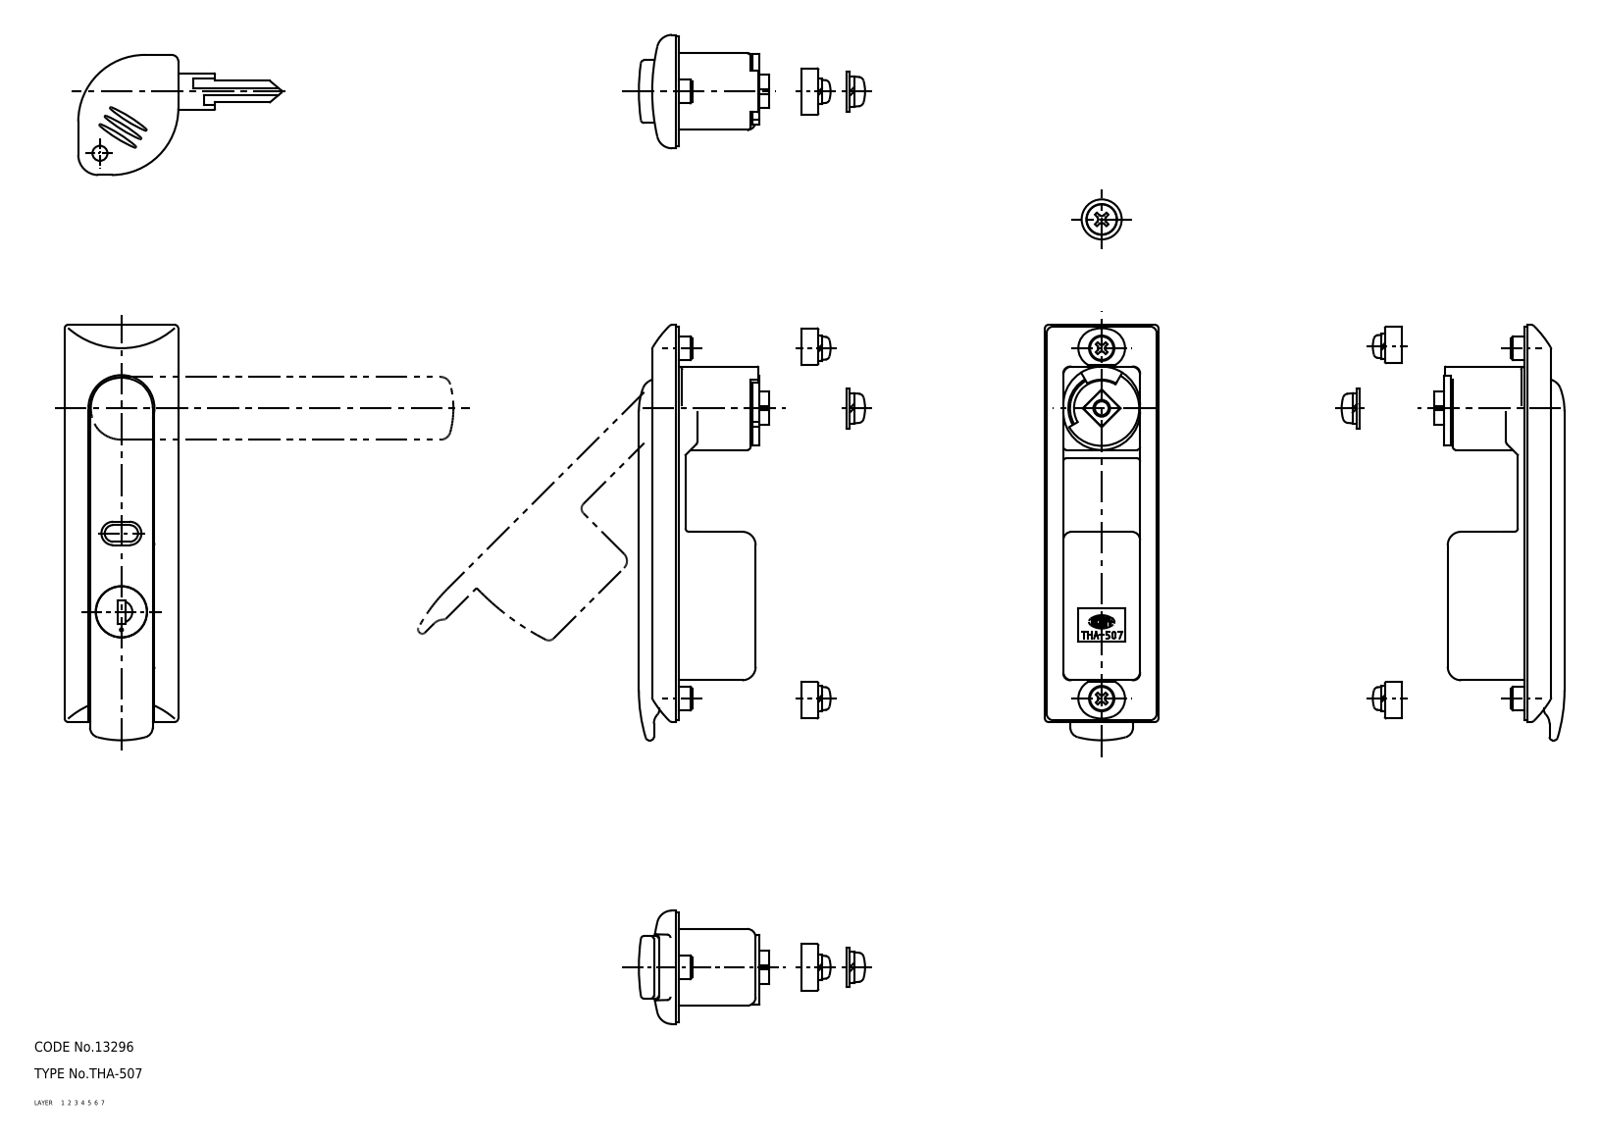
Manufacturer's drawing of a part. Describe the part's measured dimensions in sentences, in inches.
The part is named "67135846; 67135859; 67135872; 67135885 (+7 more)". Its 3-D file was written by "CADfix (AUTOMOTIVE_DESIGN)". It is 11 solids with 432 faces: 0 planar, 0 cylindrical and 432 other. Overall it measures 5.703 by 4.902 by 1.339 inches. Its volume is 4.371 cubic inches and its surface area 64.13 square inches.
